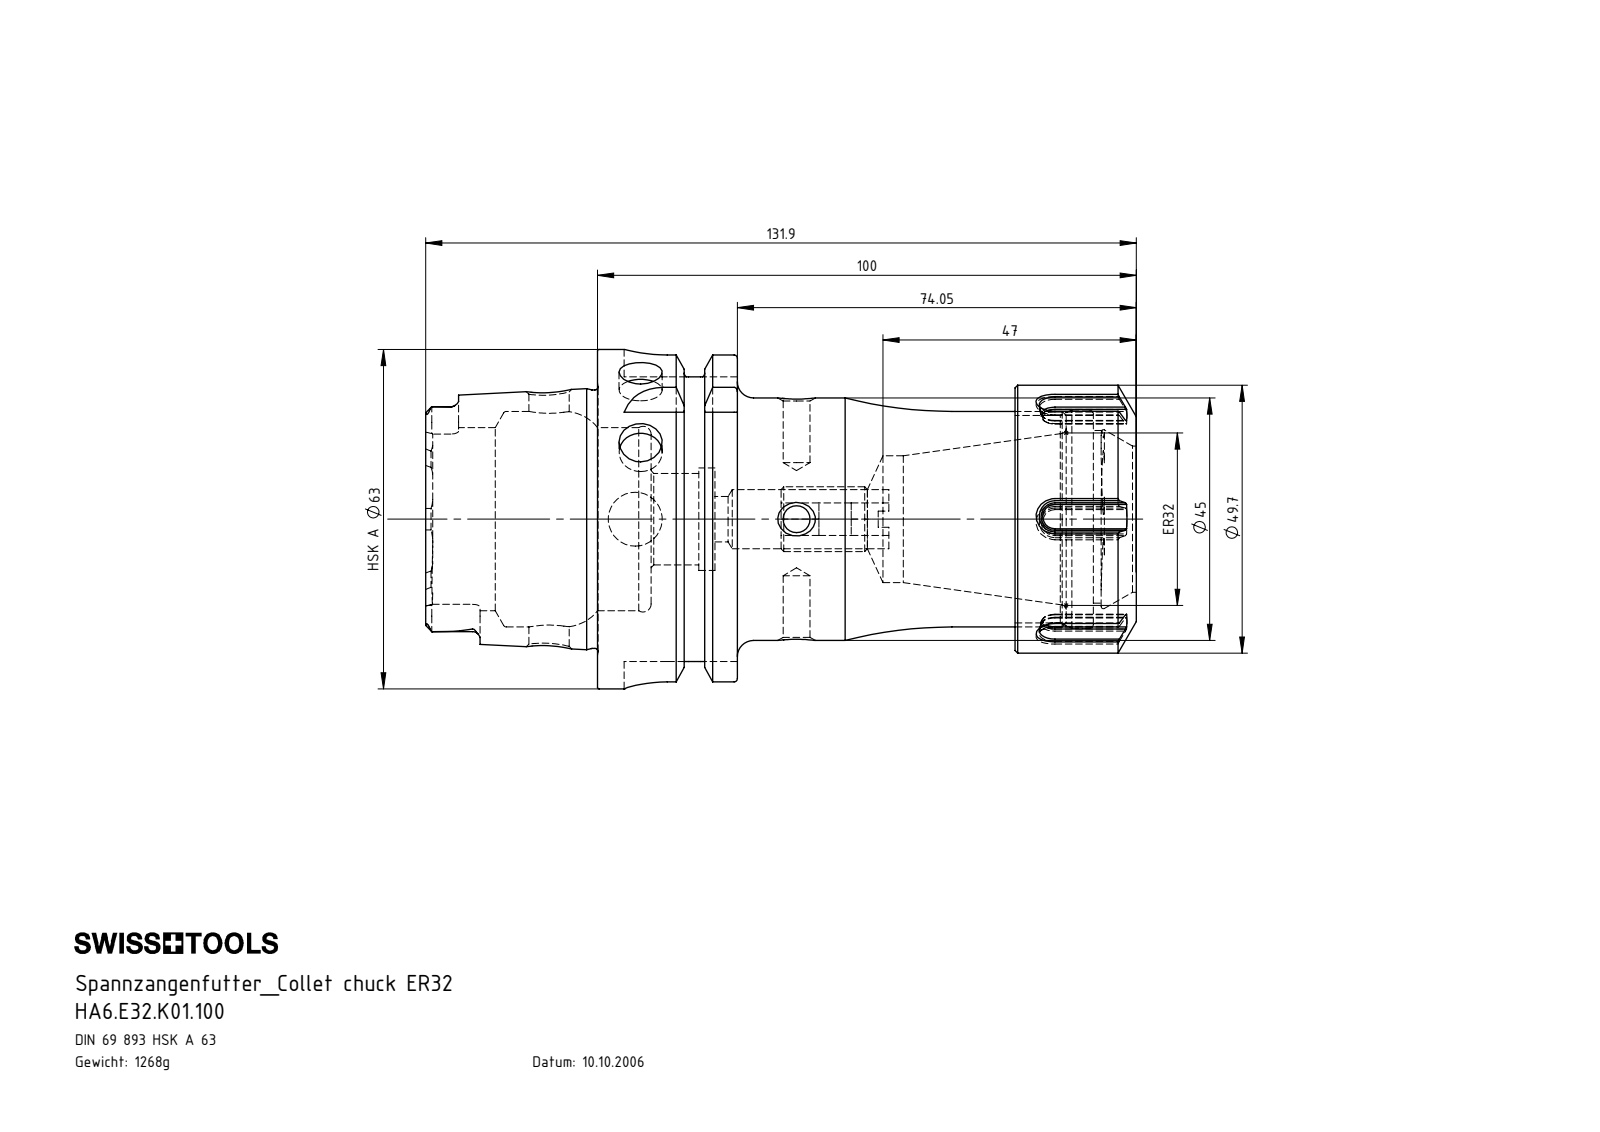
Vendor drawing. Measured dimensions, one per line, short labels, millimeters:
name: HA6.E32.K01.100; ERU-AN5.K01.020_A; E32-ER1.001.022; HA6-E32.K01.100_C_gewinde
written by: SolidWorks 2017 (AUTOMOTIVE_DESIGN)
unit: mm
bodies: 3 solids, 296 faces (133 planar, 63 cylindrical, 100 other)
size: 131.9 × 63 × 63
volume: 160 998 mm³; area: 45 197 mm²
holes: 2× ⌀5, 2× ⌀8, 1× ⌀6, 1× ⌀7.5, 1× ⌀8.4, 1× ⌀10, 1× ⌀11, 1× ⌀17, 1× ⌀19, 1× ⌀23.5, 1× ⌀27.1, 1× ⌀34
bosses: 1× ⌀63, 1× ⌀54.95, 1× ⌀49.7, 1× ⌀47.94, 1× ⌀45, 1× ⌀40, 1× ⌀12
rounds: 6× R1.4, 4× R2.88, 4× R8, 2× R15.5
face distances: 25.95, 77.5, 51.55, 16, 100, 74.05, 22.5, 67.55, 9.95, 90.05
hole spacings: 29.95, 45.95
